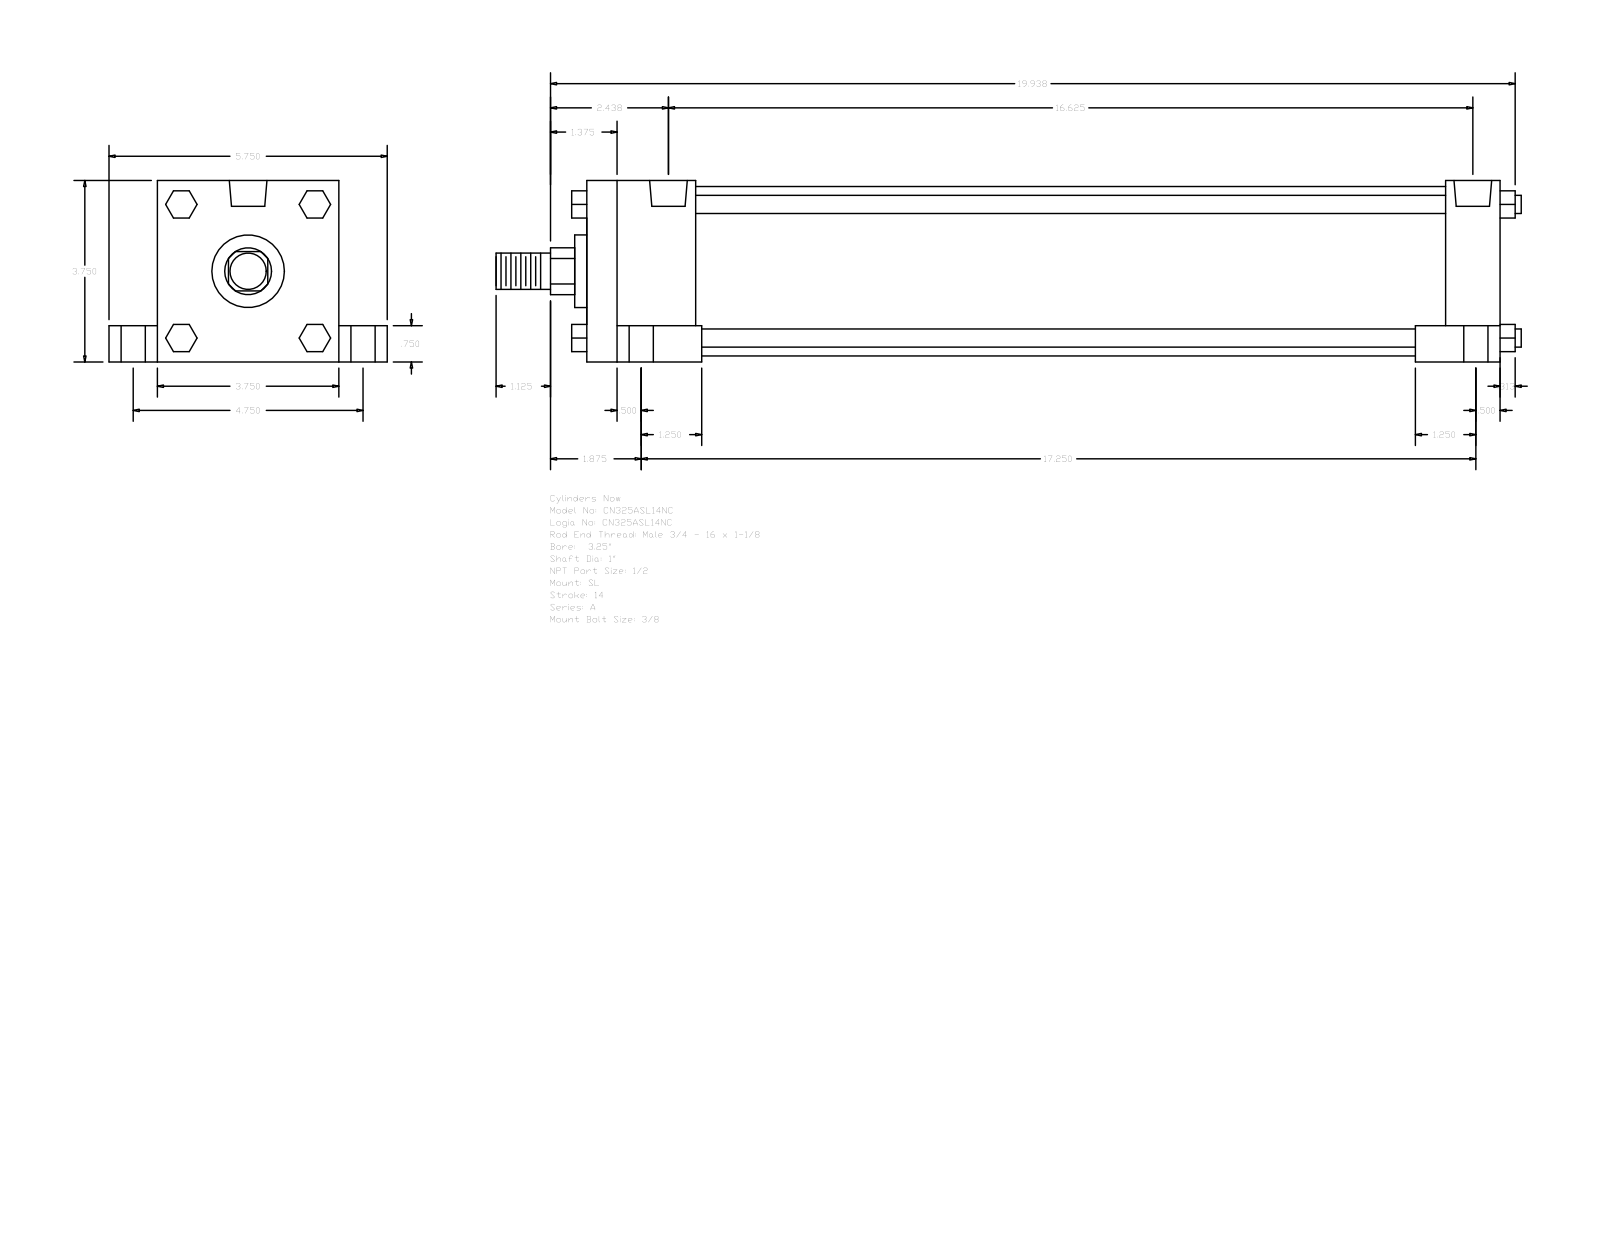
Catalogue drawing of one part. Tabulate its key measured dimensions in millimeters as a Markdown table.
| quantity | value |
| --- | --- |
| part name | A_SL__0325_1 |
| STEP written by | GSSL Pune (CONFIG_CONTROL_DESIGN) |
| units | millimeters |
| bodies | 0 solids, 150 faces (114 planar, 36 cylindrical, 0 other) |
| overall size | 538.16 × 146.05 × 95.25 |
| round holes (diameter × count) | 8.73 × 4, 12.7 × 4, 19.05 × 4, 19.77 × 2 |
| round bosses / shafts (diameter × count) | 9.53 × 4, 88.9 × 1, 38.1 × 1, 25.4 × 1, 19.05 × 1 |
| partial cylindrical surfaces (radius × count) | 12.29 × 1 |
| main face-to-face distances | 95.24, 479.43, 19.05, 25.41, 120.65, 76.19, 57.15, 450.85, 393.7, 422.28 |
| hole center spacings | 3.18, 60.35, 60.52, 62, 62.81, 120.66, 415.92, 419.1 |
